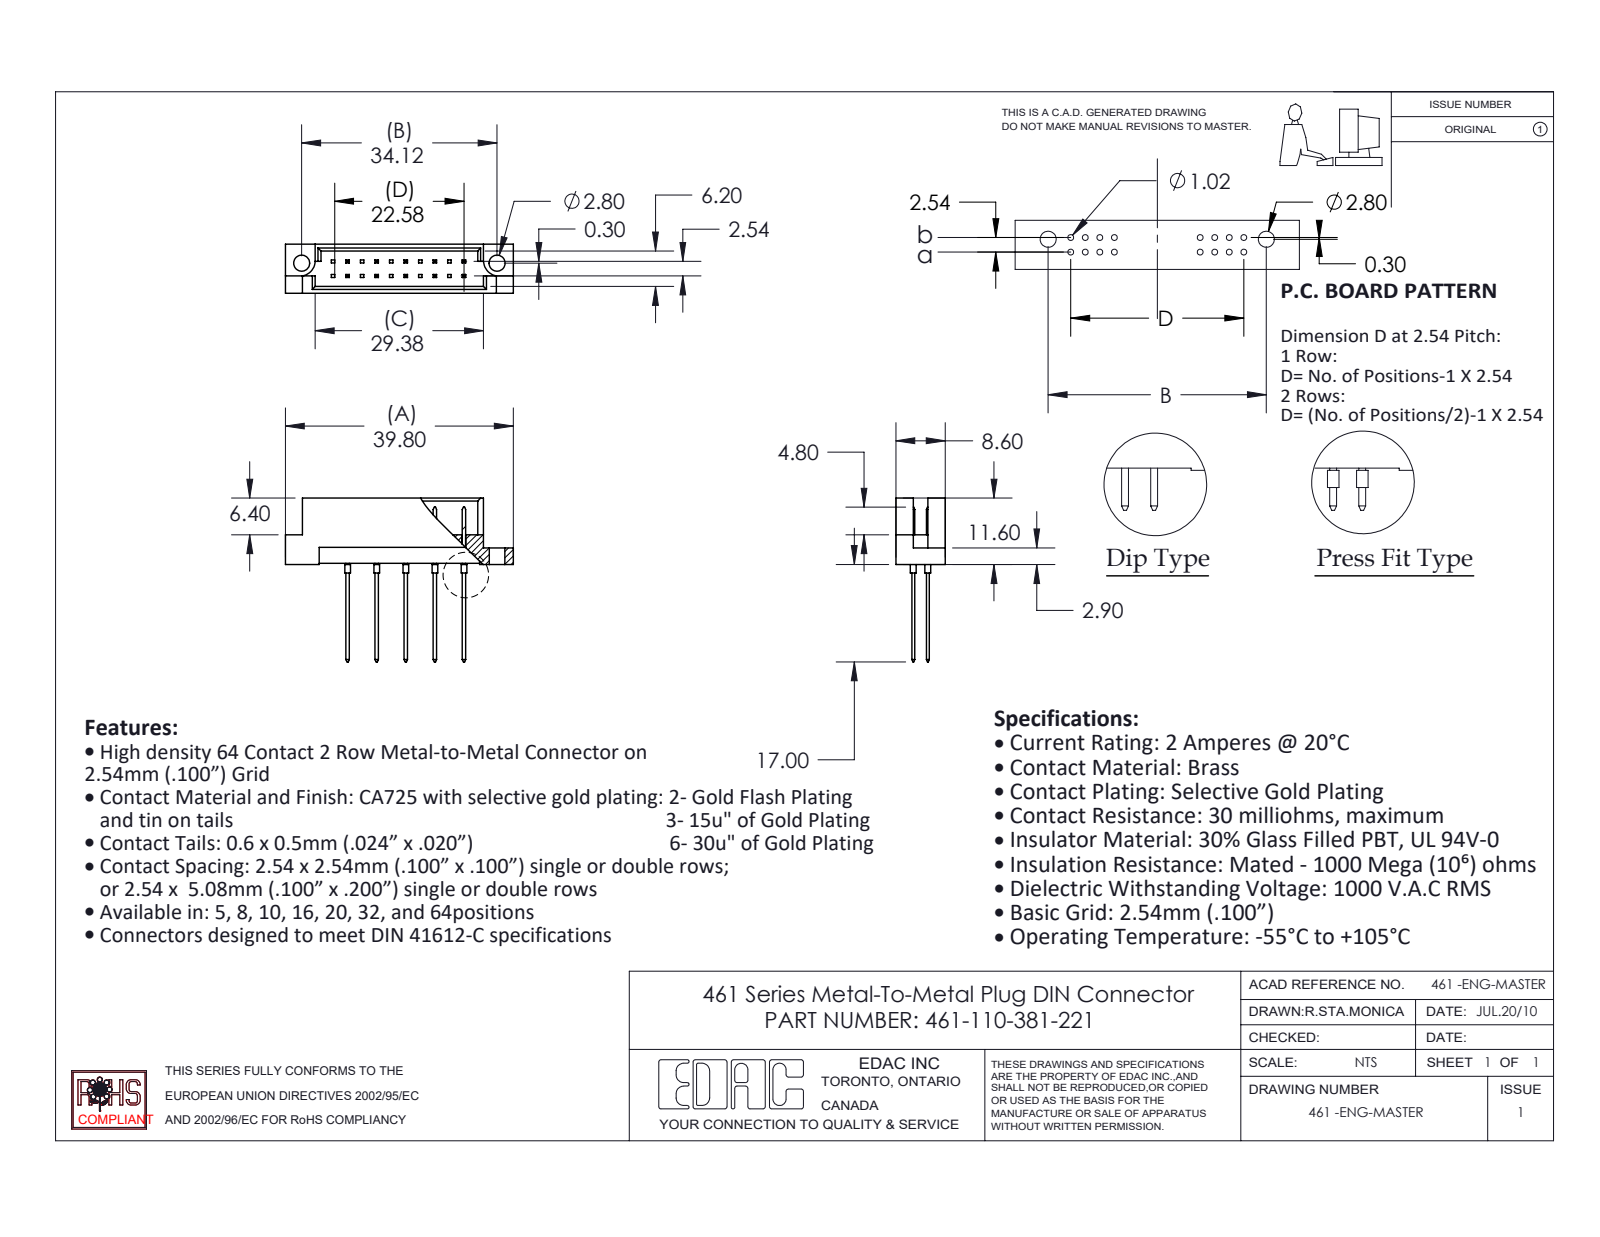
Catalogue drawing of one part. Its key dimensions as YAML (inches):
part_name: "461 Part_20; 461-290_81; 461-110-381-221"
step_written_by: "SolidWorks 2020 (CONFIG_CONTROL_DESIGN)"
units: inches
bodies: {solids: 11, faces: 348, planar: 322, cylindrical: 26, other: 0}
overall_size: [1.567, 1.126, 0.339]
volume: 0.122
surface_area: 4.576
round_holes:
  - {diameter: 0.11, count: 2}
round_bosses_or_shafts:
  - {diameter: 0.039, count: 10}
partial_cylinders:
  - {radius: 0.11, count: 2}
face_to_face_distances: [0.047, 0.291, 0.339, 0.244, 0.2, 0.1, 0.109, 0.129, 0.209, 0.229]
hole_center_spacings: [1.343]
